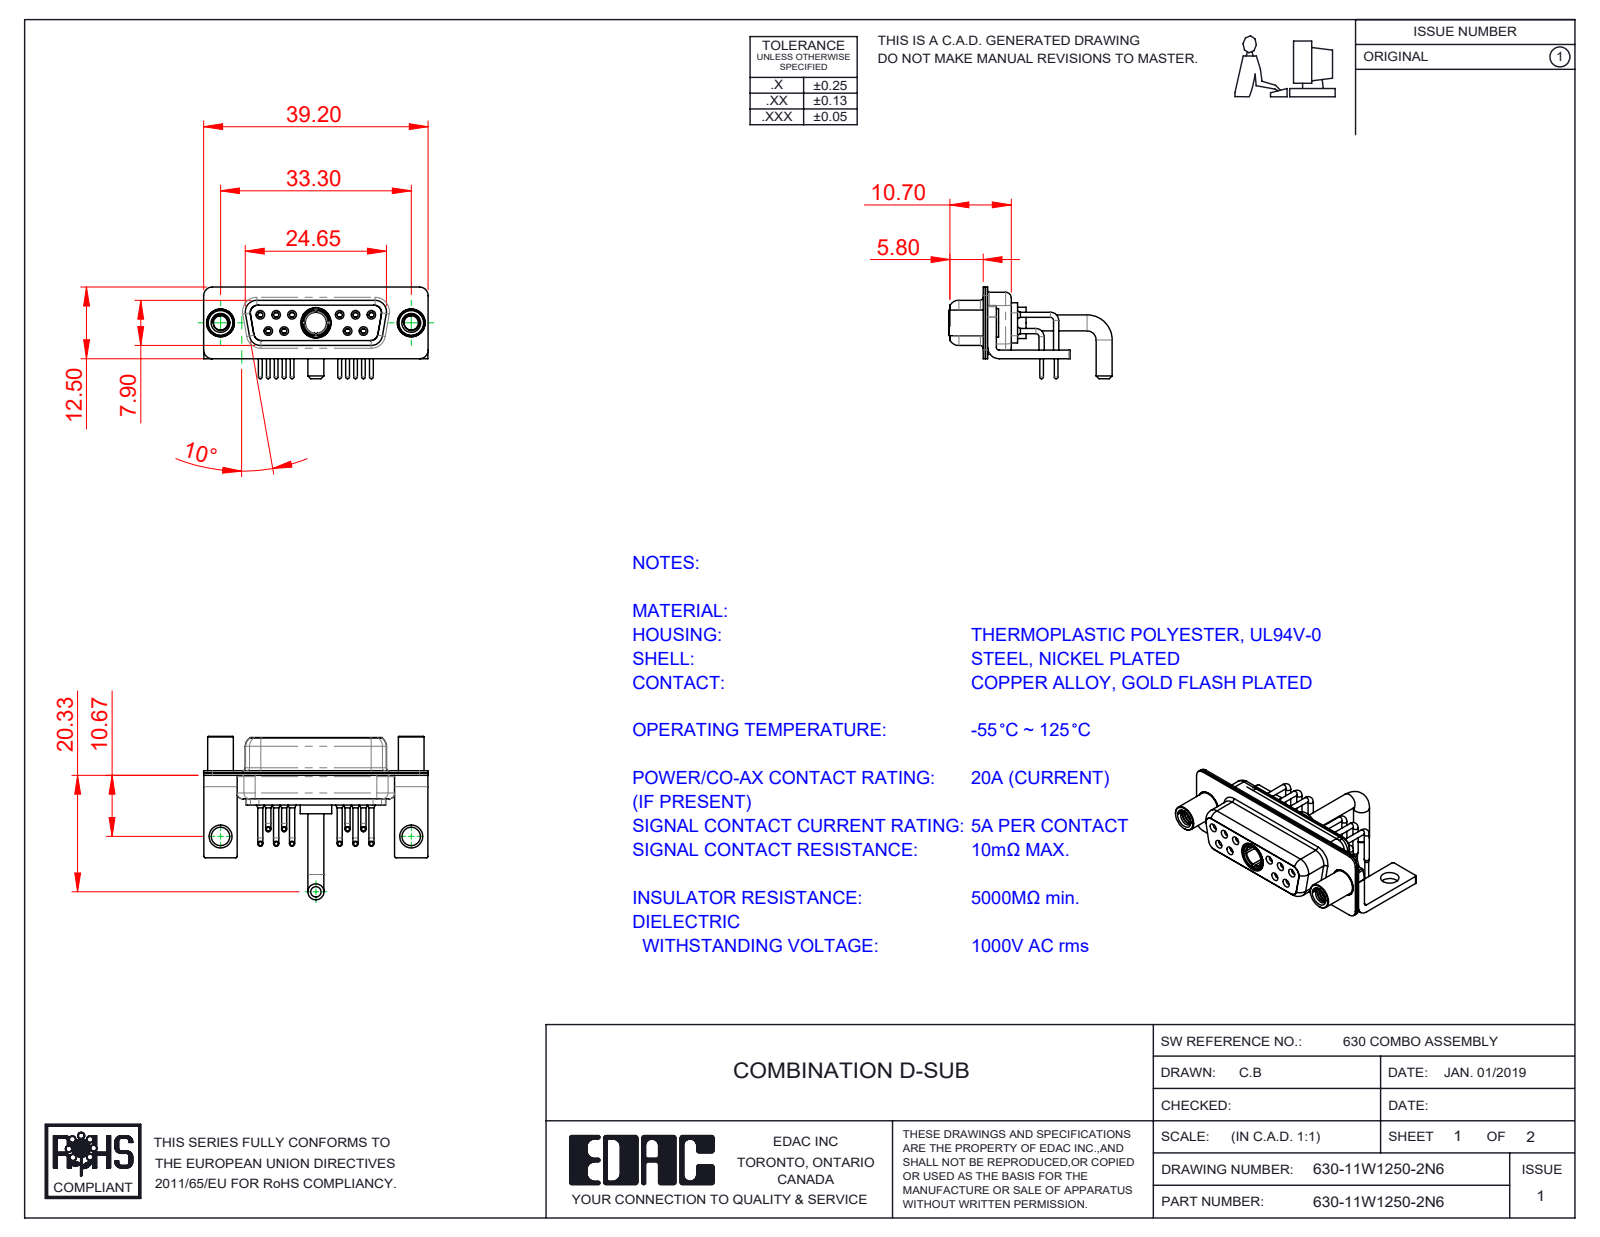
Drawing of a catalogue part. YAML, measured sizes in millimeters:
part_name: "630Combo Contact Row 2; 630-11W1250-2N6; 630Combo Threaded Standoff_D; 630Combo Shell Rear_15 Contacts (+5 more)"
step_written_by: "SolidWorks 2020 (CONFIG_CONTROL_DESIGN)"
units: millimeters
bodies: {solids: 19, faces: 985, planar: 268, cylindrical: 464, other: 253}
overall_size: [39.2, 28.53, 16]
volume: 3074
surface_area: 7259
round_holes:
  - {diameter: 0.9, count: 10}
  - {diameter: 1.1, count: 10}
  - {diameter: 1.5, count: 10}
  - {diameter: 2, count: 10}
  - {diameter: 1.7, count: 6}
  - {diameter: 1.6, count: 4}
  - {diameter: 4.85, count: 3}
  - {diameter: 2.5, count: 2}
  - {diameter: 3.2, count: 2}
  - {diameter: 4, count: 2}
  - {diameter: 4.05, count: 2}
  - {diameter: 3.7, count: 1}
round_bosses_or_shafts:
  - {diameter: 0.9, count: 10}
  - {diameter: 0.65, count: 10}
  - {diameter: 1.6, count: 6}
  - {diameter: 5, count: 2}
  - {diameter: 4.95, count: 2}
  - {diameter: 4.8, count: 2}
  - {diameter: 4.5, count: 2}
  - {diameter: 2.8, count: 2}
partial_cylinders:
  - {radius: 0.25, count: 16}
  - {radius: 1.5, count: 16}
  - {radius: 2, count: 13}
  - {radius: 1.35, count: 12}
  - {radius: 1.6, count: 8}
  - {radius: 0.5, count: 5}
  - {radius: 0.6, count: 4}
  - {radius: 0.65, count: 4}
face_to_face_distances: [0.4, 0.8, 1.4, 0.45, 8.45, 1.5, 1.8, 8.9, 6.2, 2.3]
hole_center_spacings: [3.16, 2.77, 13.85, 11.08, 16.62, 5.03, 5.04, 5.54]
